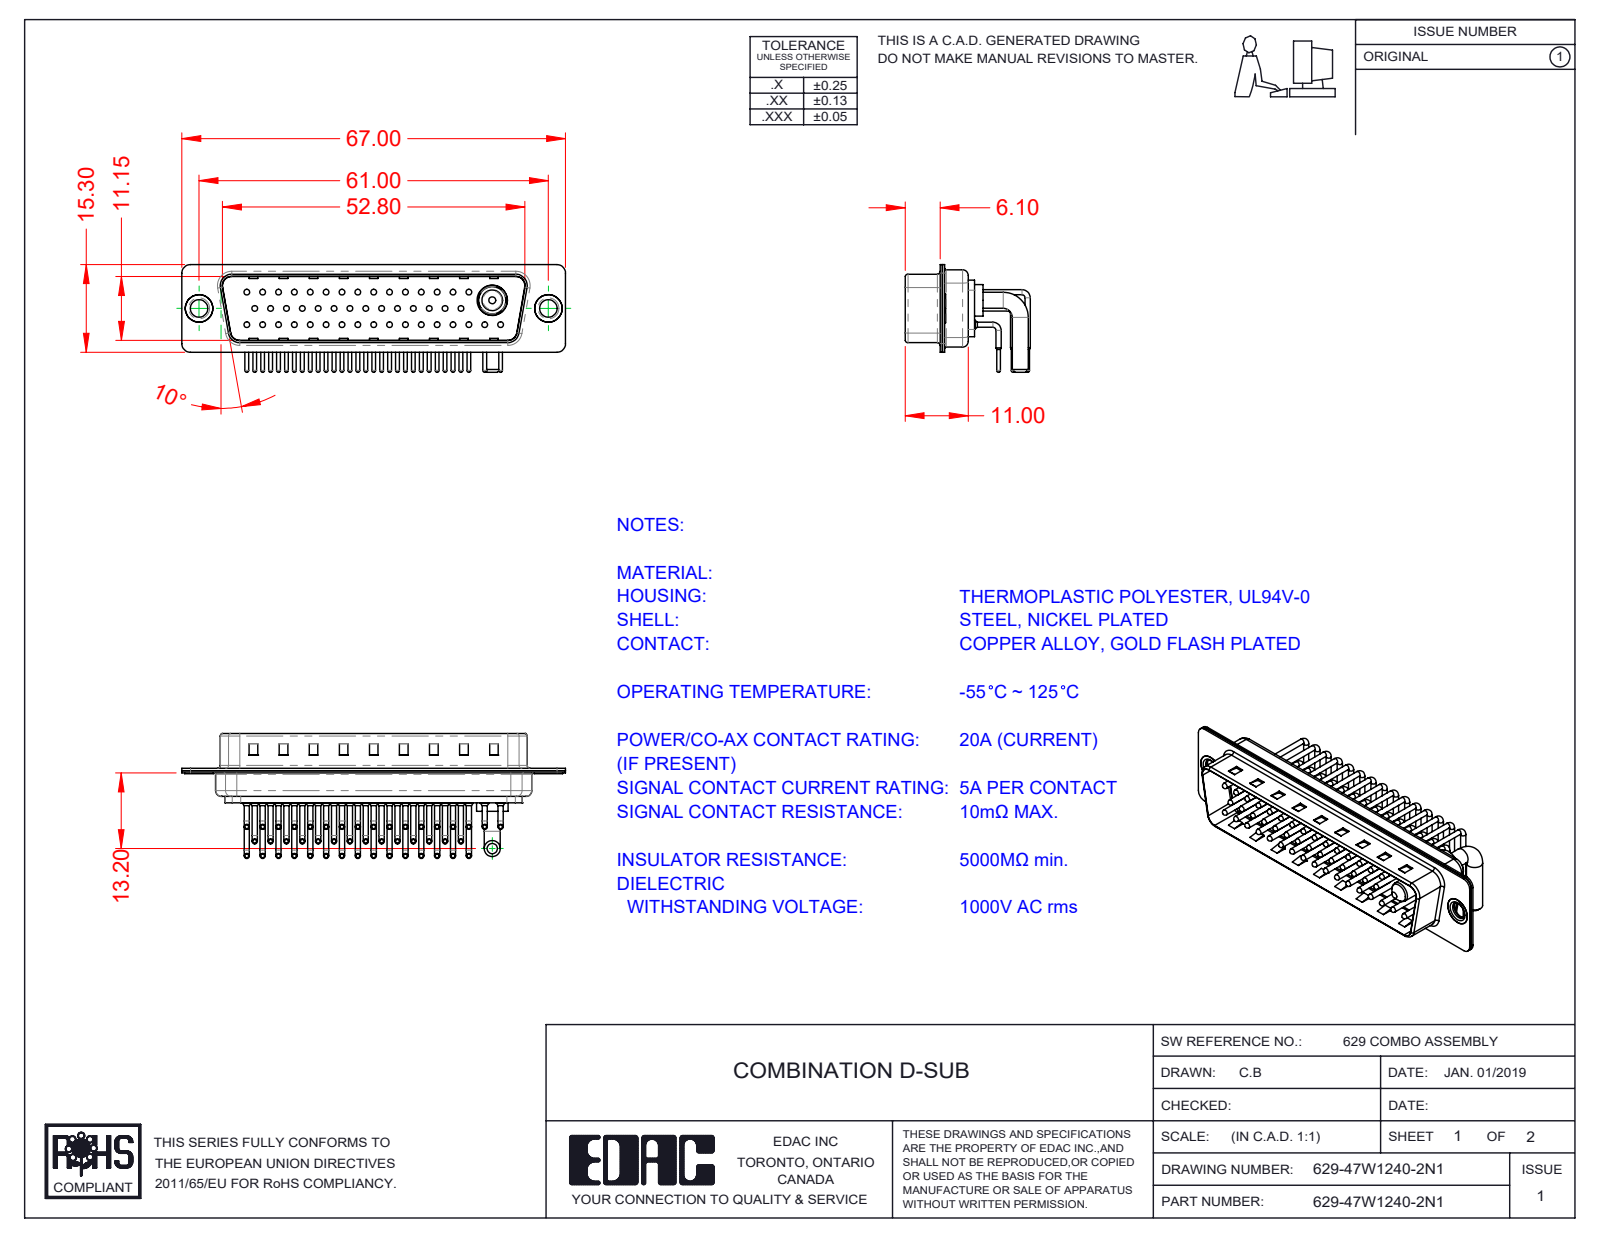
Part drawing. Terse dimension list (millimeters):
name: 629Combo Shell Front_50 Contacts; 629Combo Thru Hole Rivet; 629Combo Contact Row 3; 629Combo Contact Row 1_50 Contacts (+5 more)
written by: SolidWorks 2020 (CONFIG_CONTROL_DESIGN)
unit: mm
bodies: 53 solids, 5489 faces (3157 planar, 1802 cylindrical, 530 other)
size: 67 × 21.83 × 18.8
volume: 5 053 mm³; area: 12 634 mm²
holes: 46× ⌀0.75, 46× ⌀1.6, 46× ⌀2, 2× ⌀3.05, 2× ⌀4, 2× ⌀4.8, 1× ⌀4.85, 1× ⌀5.3
bosses: 92× ⌀0.9, 46× ⌀1.5, 46× ⌀1, 46× ⌀0.65, 2× ⌀5, 2× ⌀4.9, 2× ⌀3.55, 2× ⌀2.8
rounds: 46× R1.01, 16× R1.5, 12× R2, 8× R0.5, 8× R1.6, 4× R0.25, 4× R0.6, 4× R0.65
face distances: 0.4, 11.55, 5.6, 4.1, 1.5, 6, 0.78, 1.1, 0.77, 12.33
hole spacings: 2.77, 3.16, 5.54, 8.31, 11.08, 13.85, 16.62, 19.39
